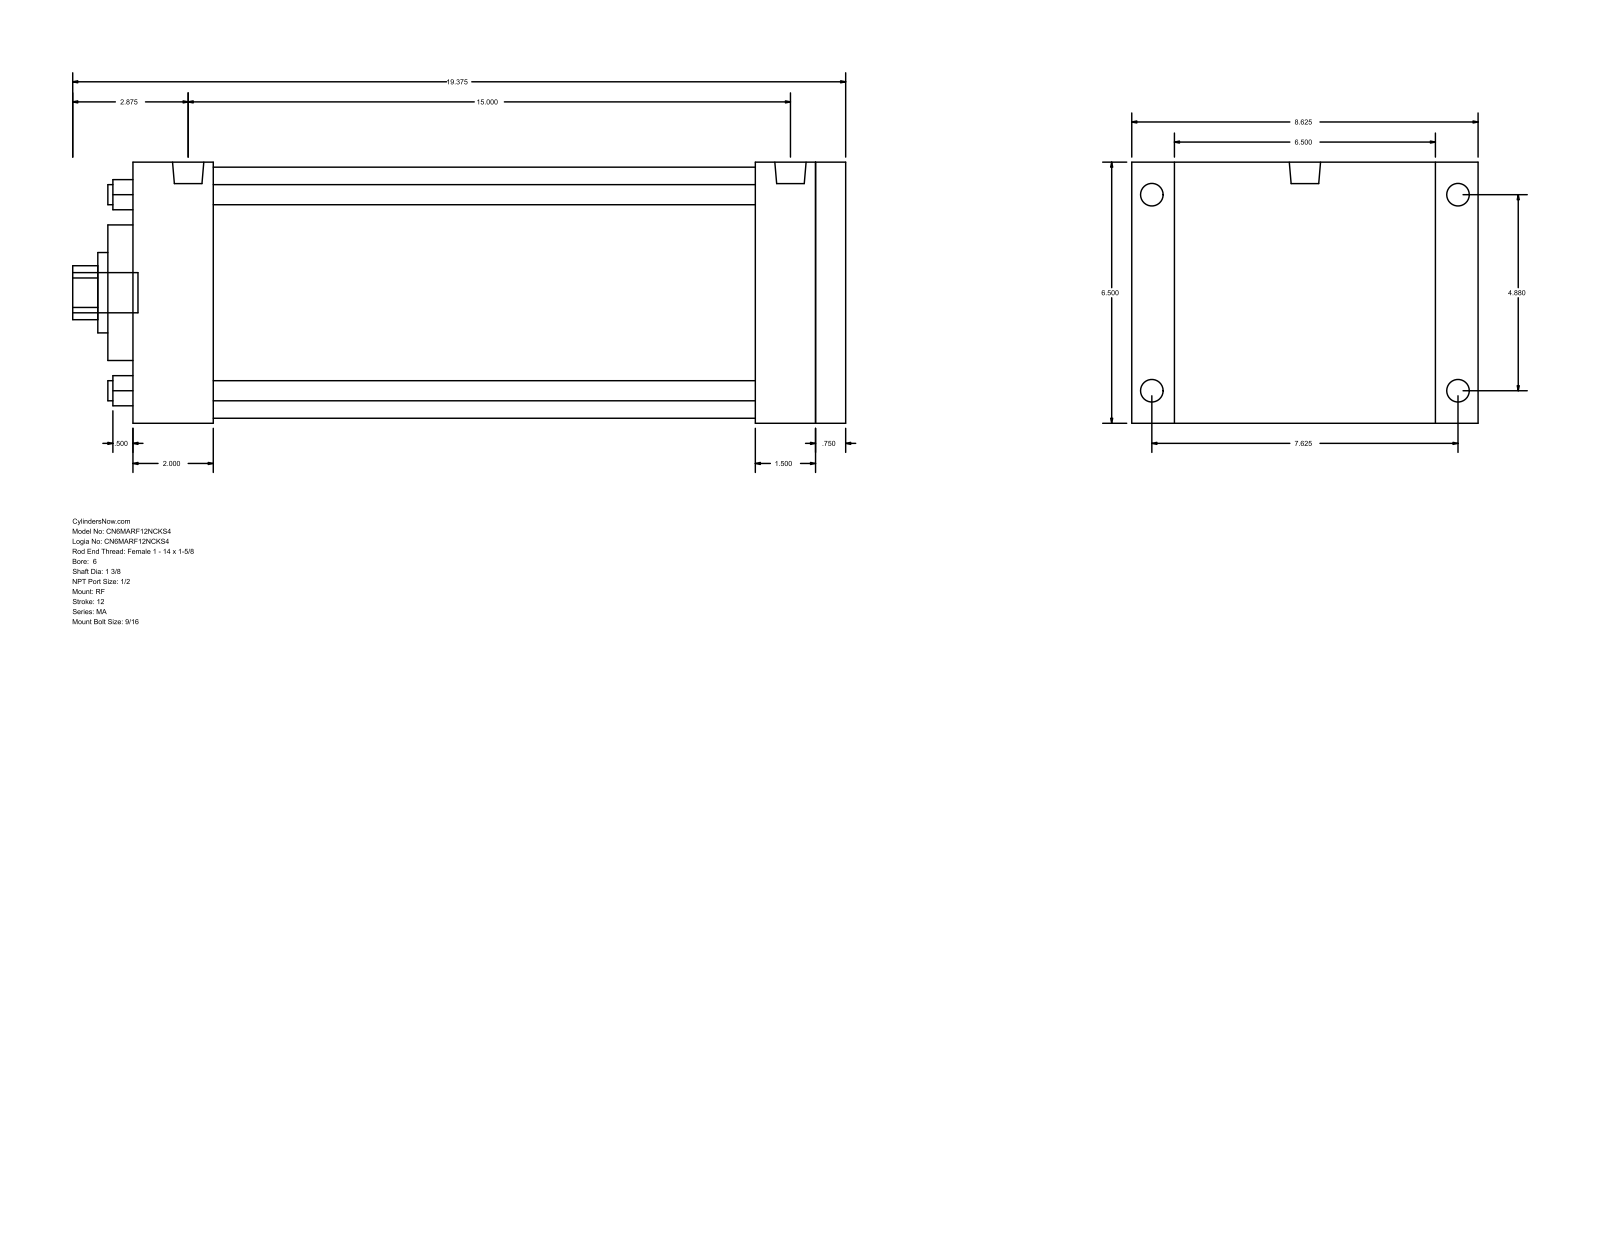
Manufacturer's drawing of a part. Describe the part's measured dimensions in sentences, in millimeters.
The part is named "MA_RF__0600_1.375". Its 3-D file was written by "GSSL Pune (CONFIG_CONTROL_DESIGN)". It is 0 solids with 94 faces: 65 planar, 29 cylindrical and 0 other. Overall it measures 492.12 by 219.07 by 165.1 millimeters. Round holes: 4 of diameter 12.7, 1 of diameter 34.92, 1 of diameter 50.8, 1 of diameter 85.72, 1 of diameter 158.75. Round bosses or shafts: 4 of diameter 17.46, 4 of diameter 14.29, 2 of diameter 19.77, 1 of diameter 25.4. Partial cylindrical surfaces (rounded edges, fillets, slot ends): 1 of radius 17.06. The main face-to-face distances are 165.1, 454.02, 19.05, 434.97, 50.8, 384.17, 403.22, 396.88, 346.08, 38.09. The hole center spacings are 87.65, 123.96, 175.31.
